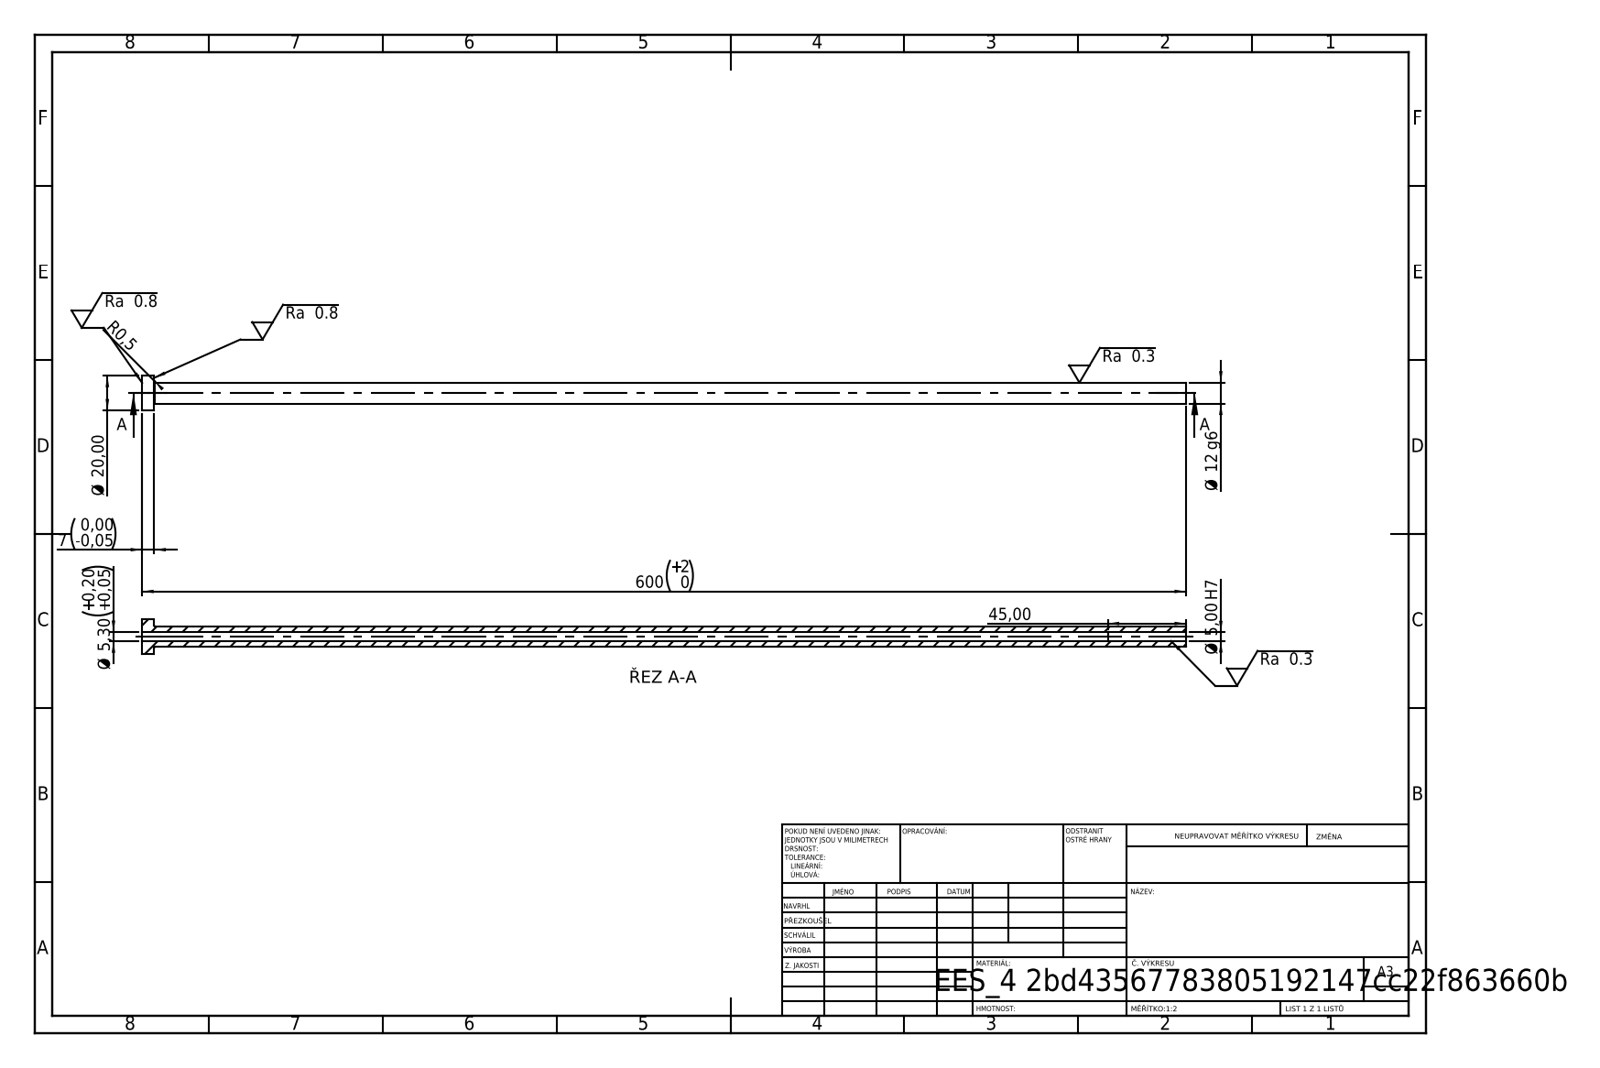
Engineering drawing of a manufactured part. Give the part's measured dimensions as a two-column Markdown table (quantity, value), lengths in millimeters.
| quantity | value |
| --- | --- |
| STEP written by | SolidWorks 2019 (CONFIG_CONTROL_DESIGN) |
| units | millimeters |
| bodies | 1 solid, 14 faces (4 planar, 8 cylindrical, 2 other) |
| overall size | 600 × 20 × 20 |
| volume | 56 140 mm³ |
| surface area | 33 324 mm² |
| round holes (diameter × count) | 5 × 1, 5.3 × 1 |
| round bosses / shafts (diameter × count) | 20 × 1, 12 × 1 |
| main face-to-face distances | 7, 600, 593, 555, 548, 45 |
